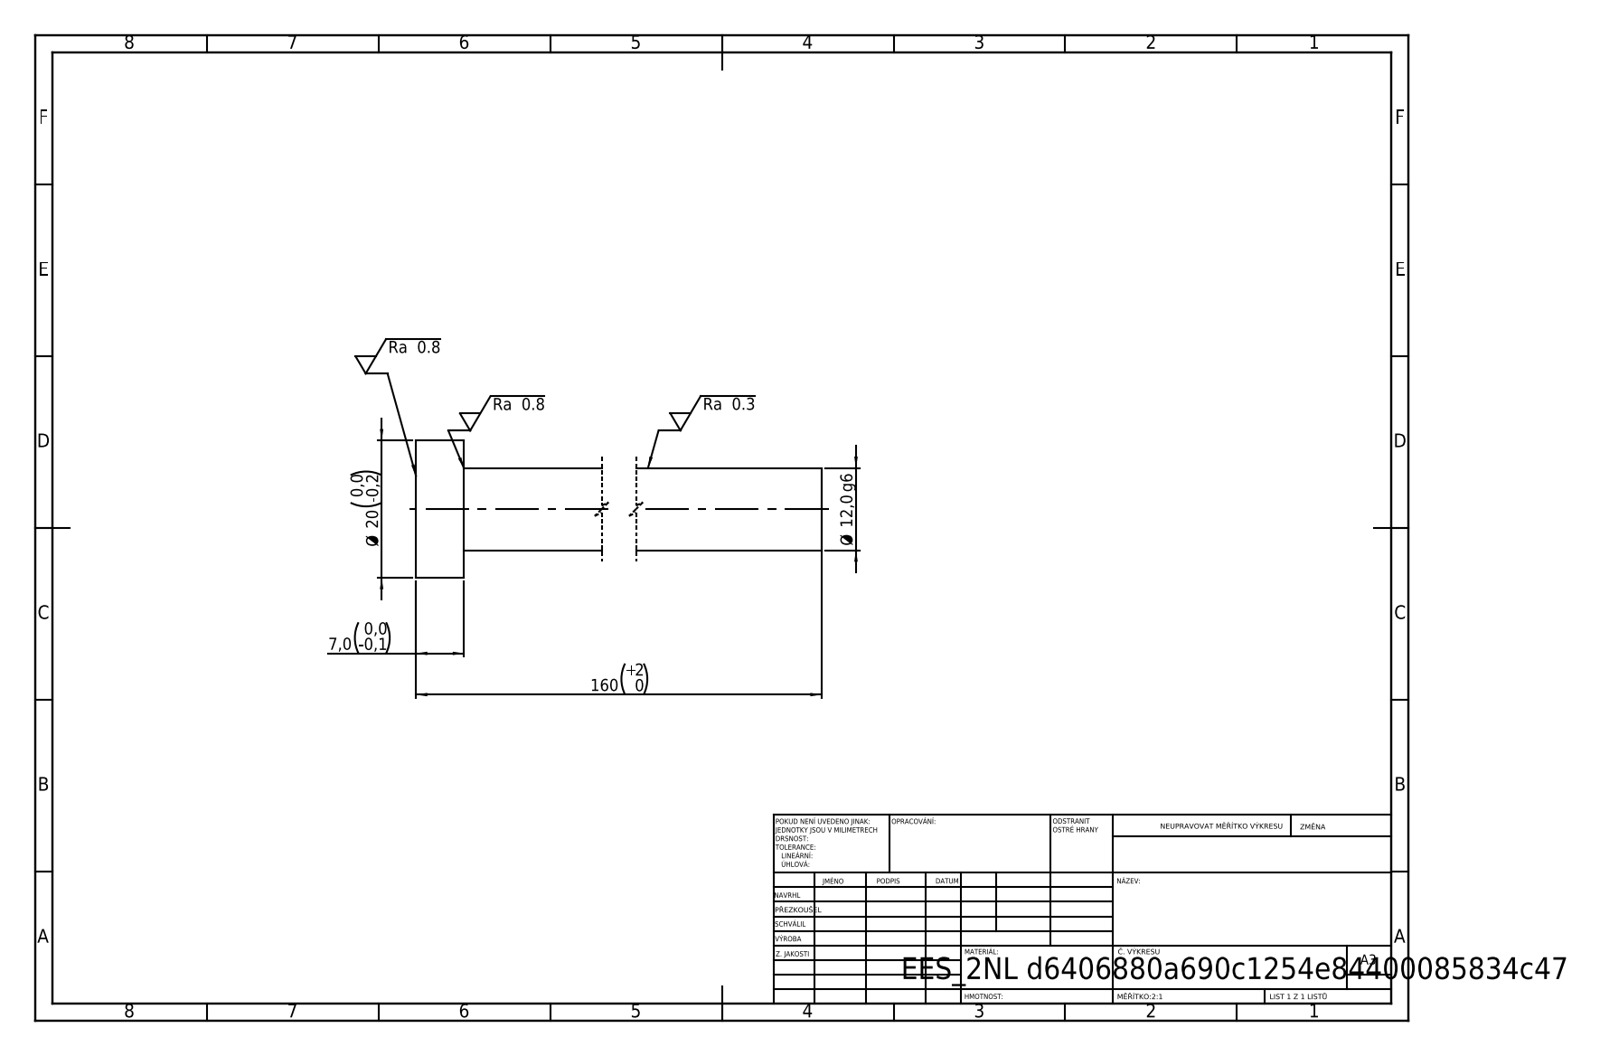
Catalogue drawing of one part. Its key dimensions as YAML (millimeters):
step_written_by: "SolidWorks 2019 (CONFIG_CONTROL_DESIGN)"
units: millimeters
bodies: {solids: 1, faces: 7, planar: 3, cylindrical: 4, other: 0}
overall_size: [160, 20, 20]
volume: 19503
surface_area: 6836
round_bosses_or_shafts:
  - {diameter: 20, count: 1}
  - {diameter: 12, count: 1}
face_to_face_distances: [7, 160, 153]
